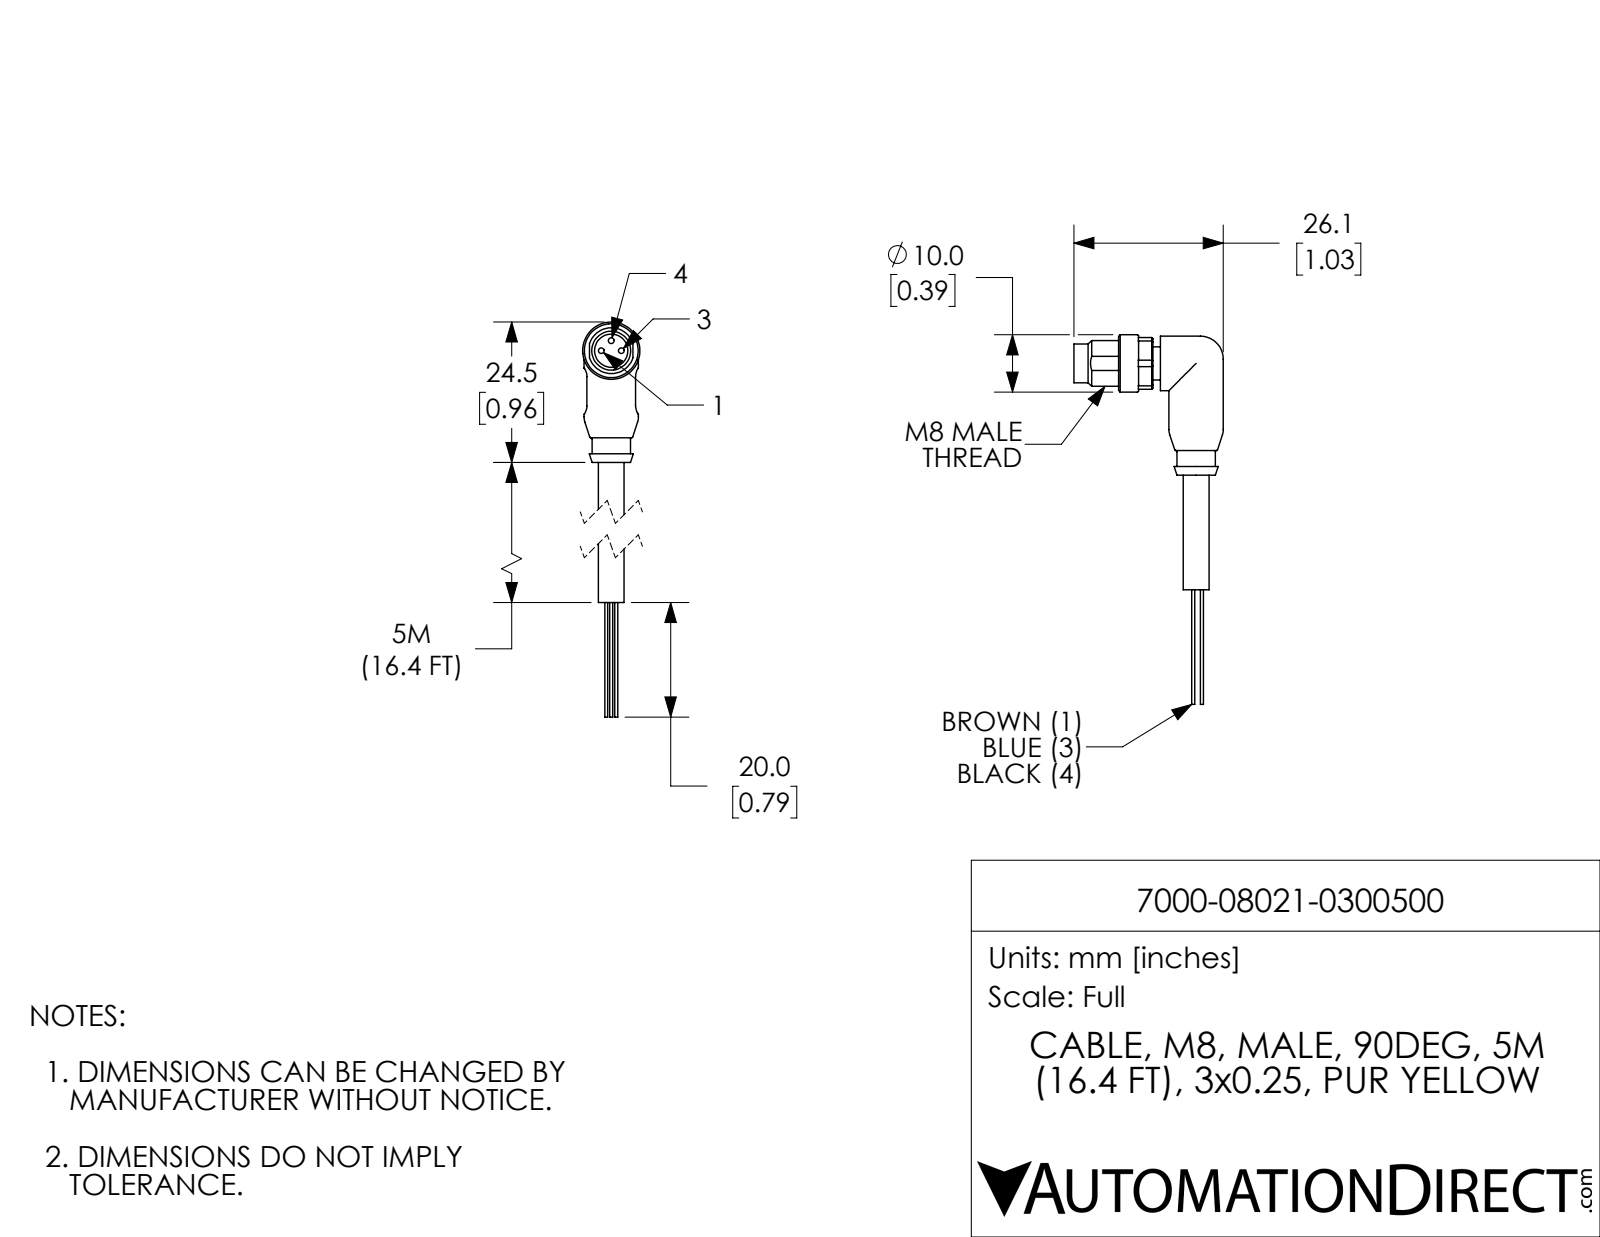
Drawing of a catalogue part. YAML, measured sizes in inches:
part_name: "7000-08021-0300500"
step_written_by: "SolidWorks 2021 (CONFIG_CONTROL_DESIGN)"
units: inches
bodies: {solids: 4, faces: 118, planar: 40, cylindrical: 45, other: 33}
overall_size: [2.539, 1.028, 0.394]
volume: 0.161
surface_area: 2.831
round_holes:
  - {diameter: 0.228, count: 1}
round_bosses_or_shafts:
  - {diameter: 0.039, count: 3}
  - {diameter: 0.02, count: 3}
  - {diameter: 0.374, count: 2}
  - {diameter: 0.394, count: 1}
  - {diameter: 0.315, count: 1}
  - {diameter: 0.268, count: 1}
  - {diameter: 0.264, count: 1}
  - {diameter: 0.177, count: 1}
partial_cylinders:
  - {radius: 0.008, count: 4}
  - {radius: 0.098, count: 4}
  - {radius: 0.193, count: 1}
face_to_face_distances: [0.051, 0.354, 0.018, 0.317, 0.346, 0.398, 0.335, 0.11, 0.236, 0.287]
